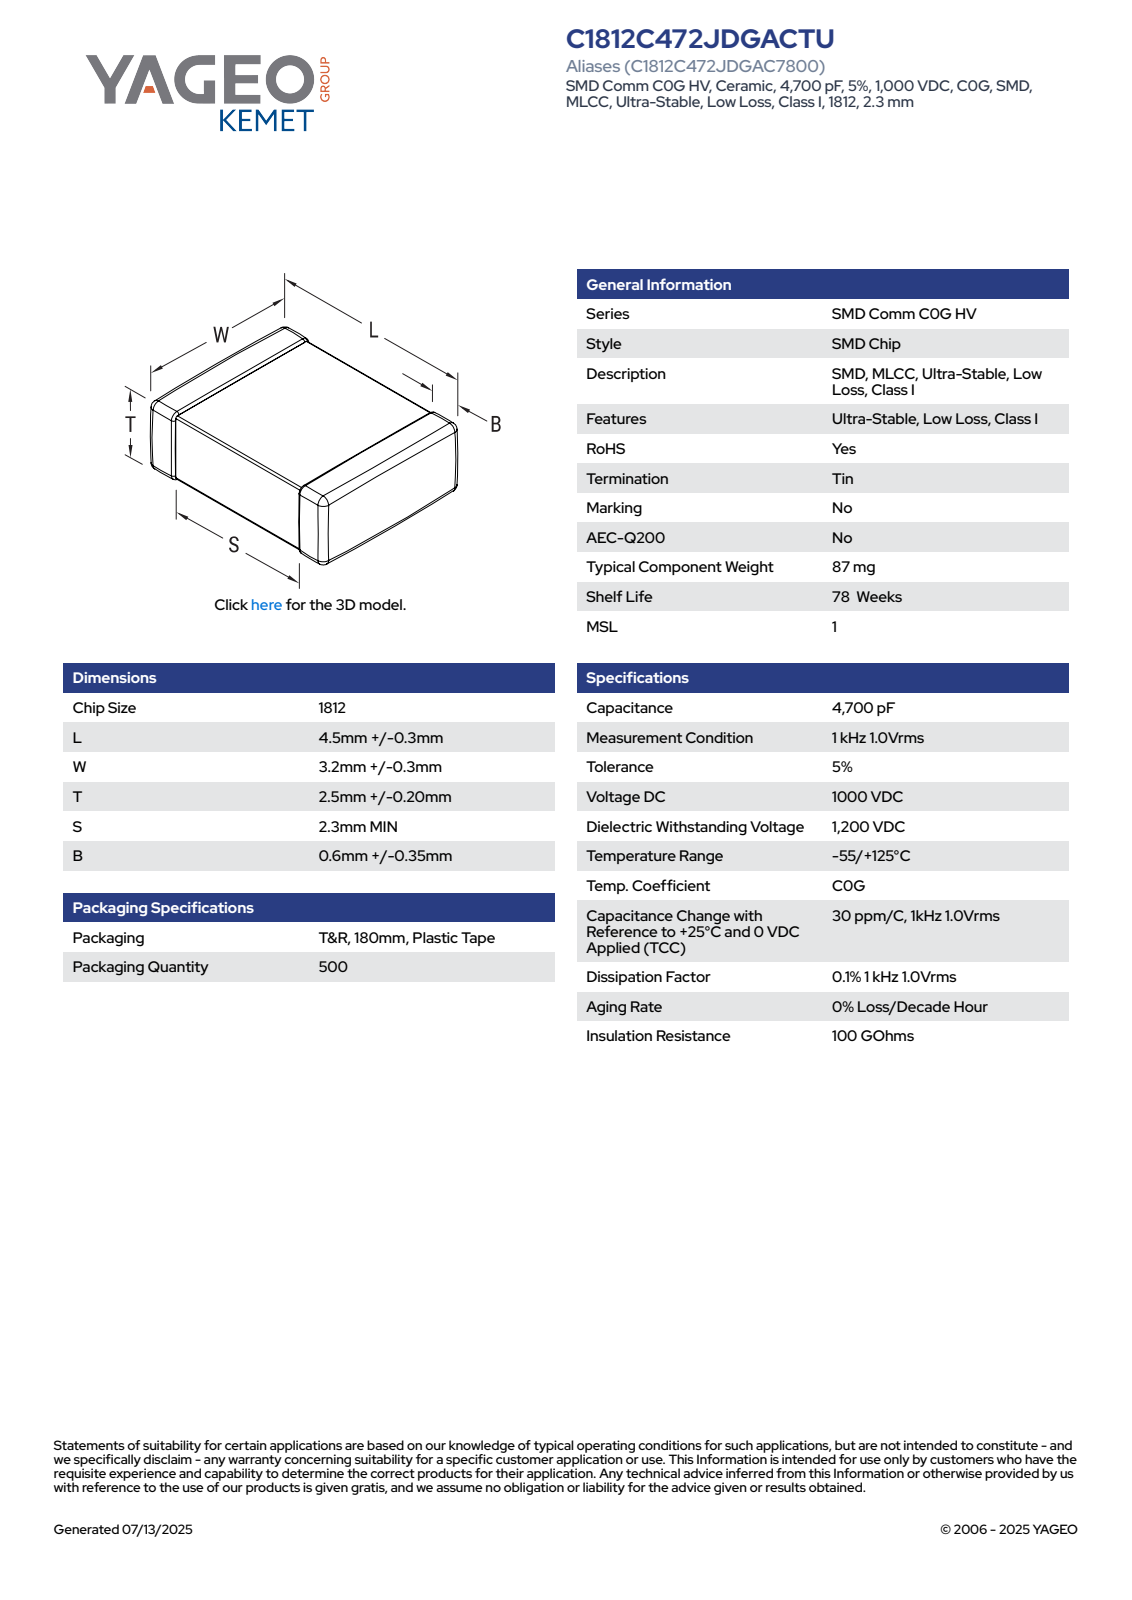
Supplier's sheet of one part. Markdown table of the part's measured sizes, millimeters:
| quantity | value |
| --- | --- |
| part name | CCS_CCSTDNOS_1812_L4.8W3.5T2.7B0.95 |
| STEP written by | SolidWorks 2014 (AUTOMOTIVE_DESIGN) |
| units | millimeters |
| bodies | 4 solids, 125 faces (71 planar, 38 cylindrical, 16 other) |
| overall size | 4.8 × 3.5 × 2.7 |
| volume | 43 mm³ |
| surface area | 77 mm² |
| main face-to-face distances | 2.63, 2.56, 4.8, 3.43, 3.36, 2.7, 3.5, 1.49, 0.34, 1.94 |
